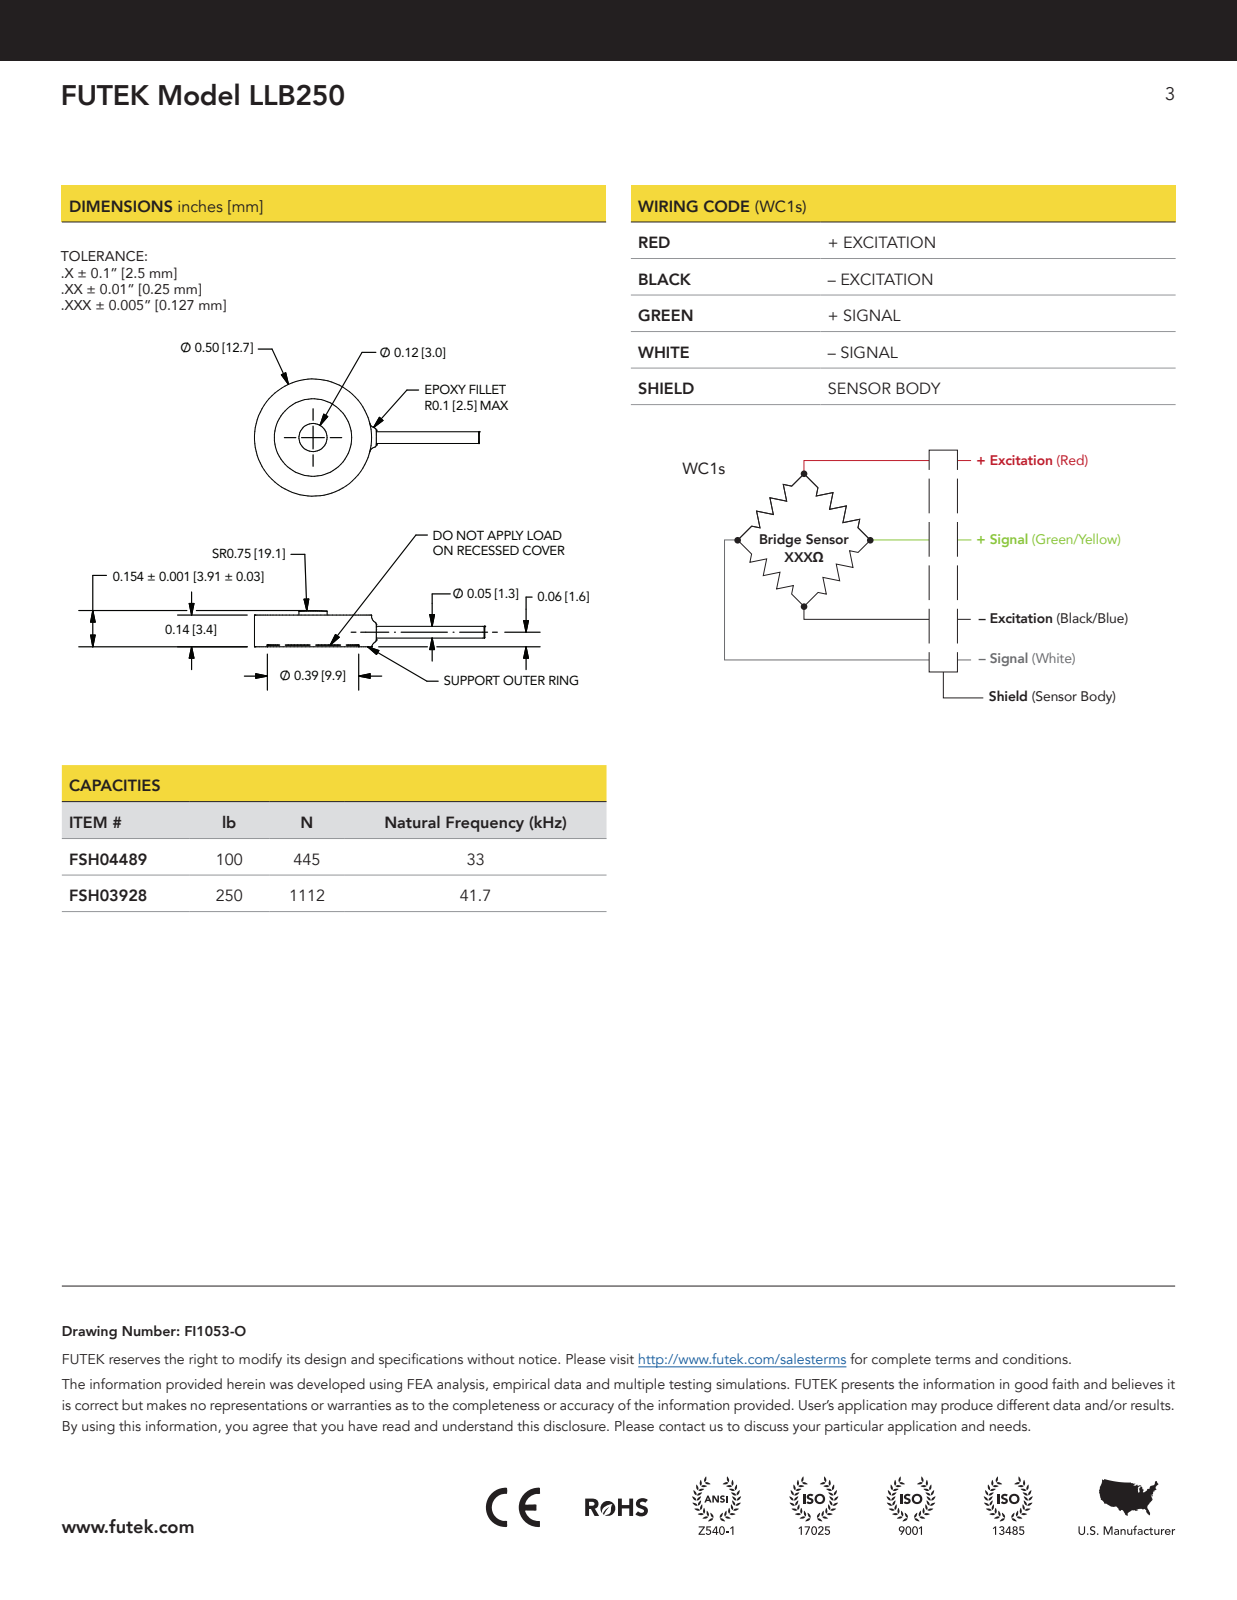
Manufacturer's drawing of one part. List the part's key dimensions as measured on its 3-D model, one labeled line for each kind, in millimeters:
Part name (STEP PRODUCT): FI1053-D
STEP written by: Mechanical Desktop 2008 (CONFIG_CONTROL_DESIGN)
Units: millimetres
Bodies: 2 solids, 35 faces (10 planar, 18 cylindrical, 7 other)
Overall size (bounding box): 16.8 × 12.7 × 3.9
Volume: 330 mm³ · Surface area: 634 mm²
Round holes (diameter × count): ⌀2.1 ×1, ⌀8.4 ×1, ⌀9.9 ×1
Round bosses / shafts (diameter × count): ⌀12.7 ×1, ⌀9.5 ×1, ⌀3 ×1, ⌀2.5 ×1, ⌀1.9 ×1
Main face-to-face distances: 3.2, 2.9, 0.5, 1.6, 3.4, 2.1, 1.9, 1.3, 3.1, 2.9
